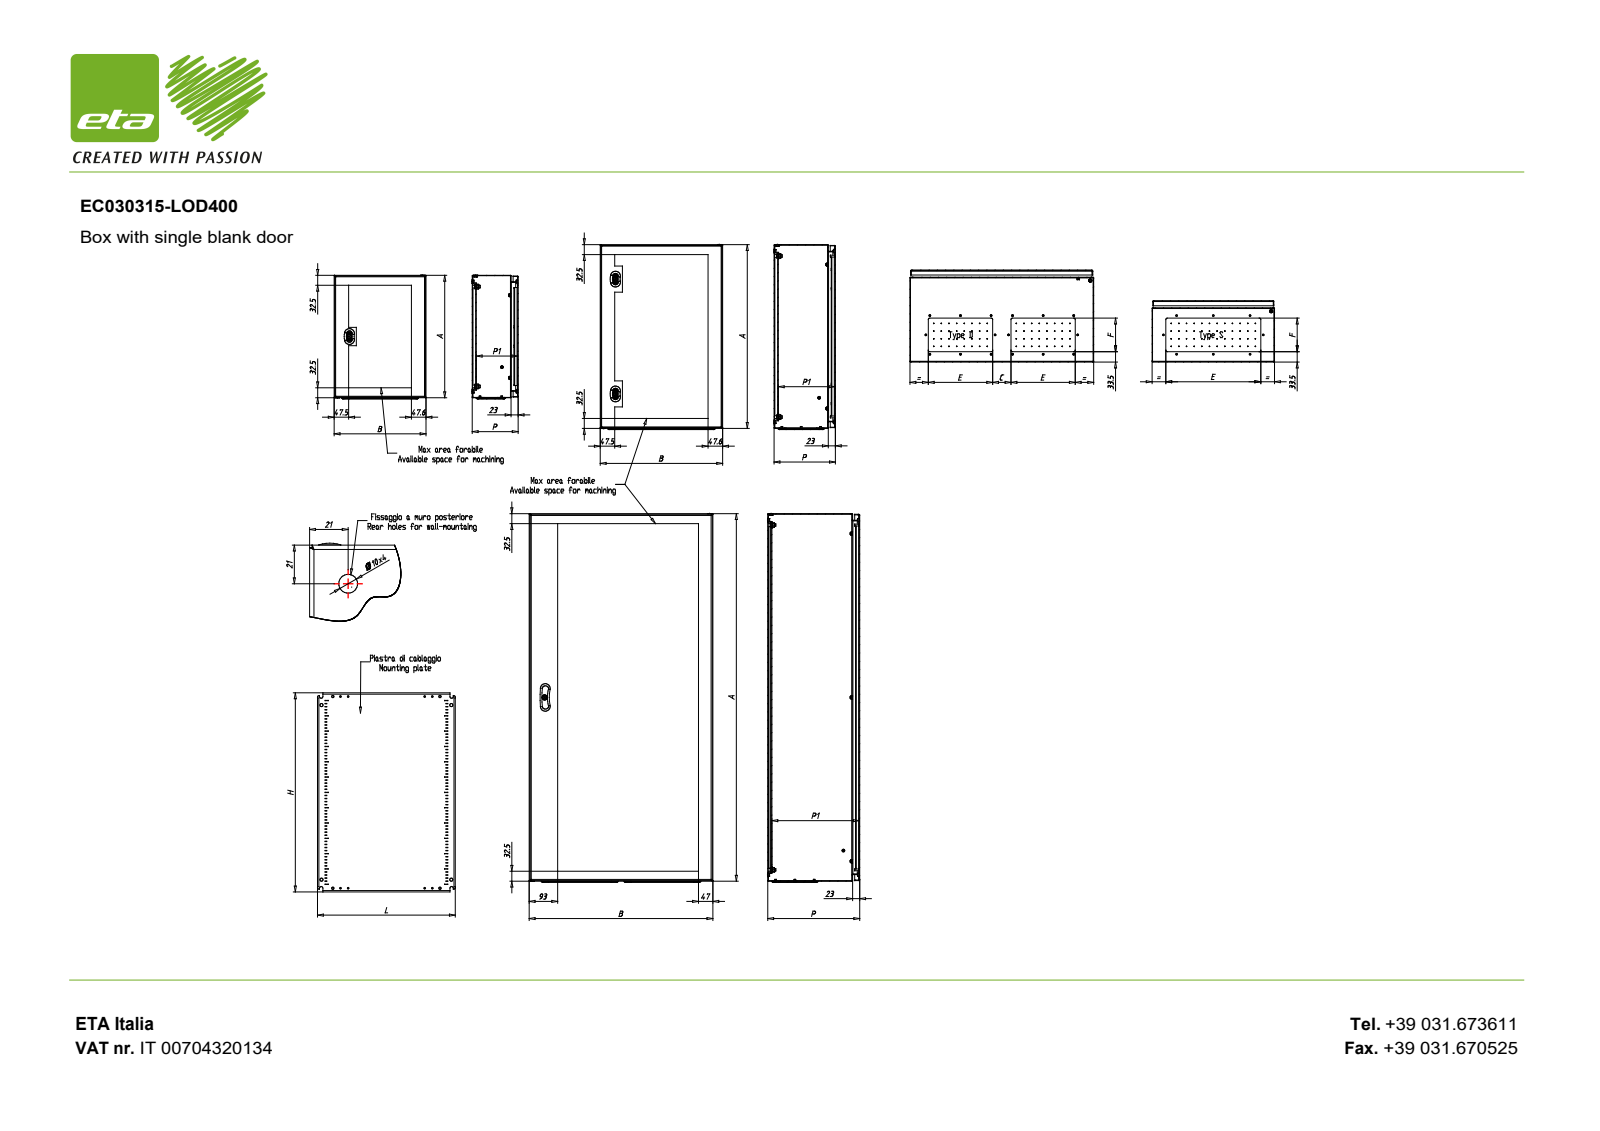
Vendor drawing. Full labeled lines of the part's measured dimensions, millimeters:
Part name (STEP PRODUCT): EC030315-LOD400; EC030315-LOD400_cabinet; EC030315-LOD400_door; EC030315-LOD400_bottom_plate (+1 more)
STEP written by: PARTsolutions (AUTOMOTIVE_DESIGN)
Units: millimetres
Bodies: 4 solids, 398 faces (162 planar, 156 cylindrical, 80 other)
Overall size (bounding box): 304 × 300 × 155
Volume: 710 772 mm³ · Surface area: 963 539 mm²
Round holes (diameter × count): ⌀4.5 ×22, ⌀1 ×16, ⌀10 ×10, ⌀5 ×4, ⌀5.5 ×4, ⌀7 ×4
Round bosses / shafts (diameter × count): ⌀8 ×7, ⌀14 ×4, ⌀6 ×3
Partial cylindrical surfaces — rounded edges, fillets, slot ends (radius × count): R2.5 ×24, R1 ×12, R5 ×12, R1.5 ×8, R0.3 ×4, R5.5 ×4, R21.5 ×4, R11 ×1
Main face-to-face distances: 1.2, 298.8, 1.5, 148.8, 150, 147.3, 148.5, 300, 12, 135.3
Hole centre spacings: 25, 50, 100, 35.36, 55.9, 75, 79.06, 125
